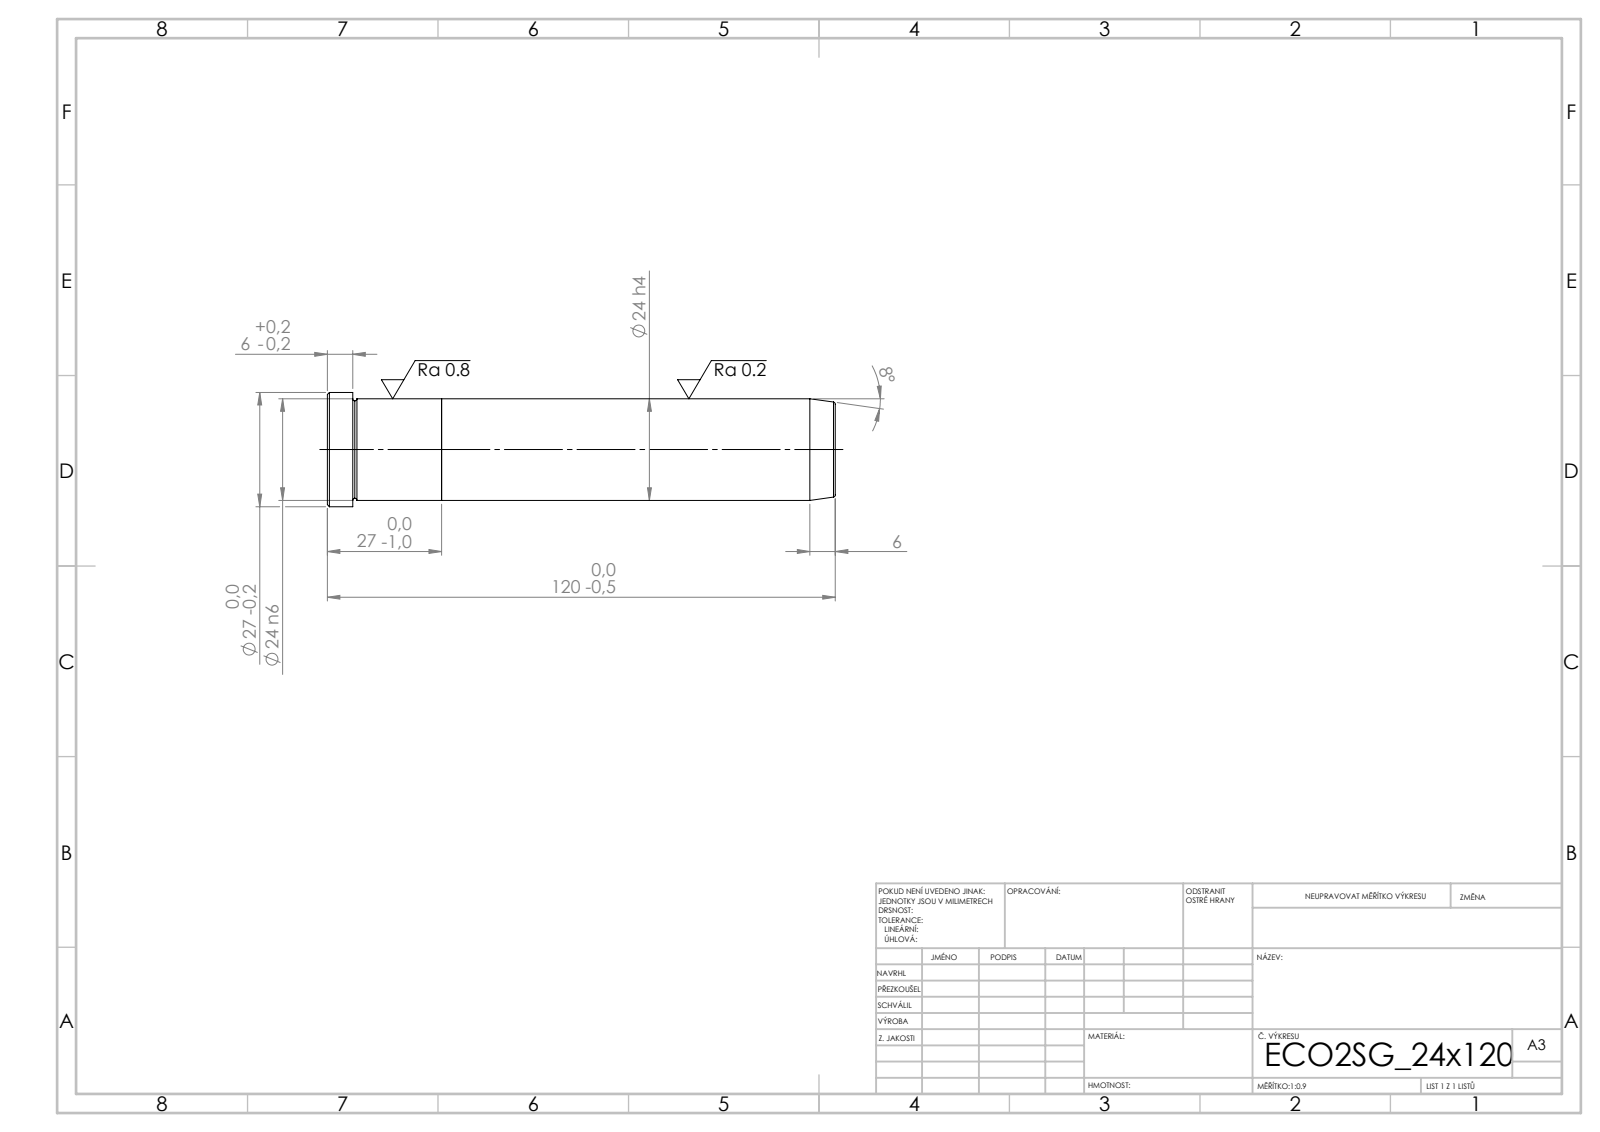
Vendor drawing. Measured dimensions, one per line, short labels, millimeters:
written by: SolidWorks 2019 (CONFIG_CONTROL_DESIGN)
unit: mm
bodies: 2 solids, 21 faces (5 planar, 6 cylindrical, 10 other)
size: 120 × 27 × 27
volume: 54 779 mm³; area: 11 085 mm²
bosses: 1× ⌀27, 1× ⌀24
face distances: 27, 93, 120, 114, 21, 6
